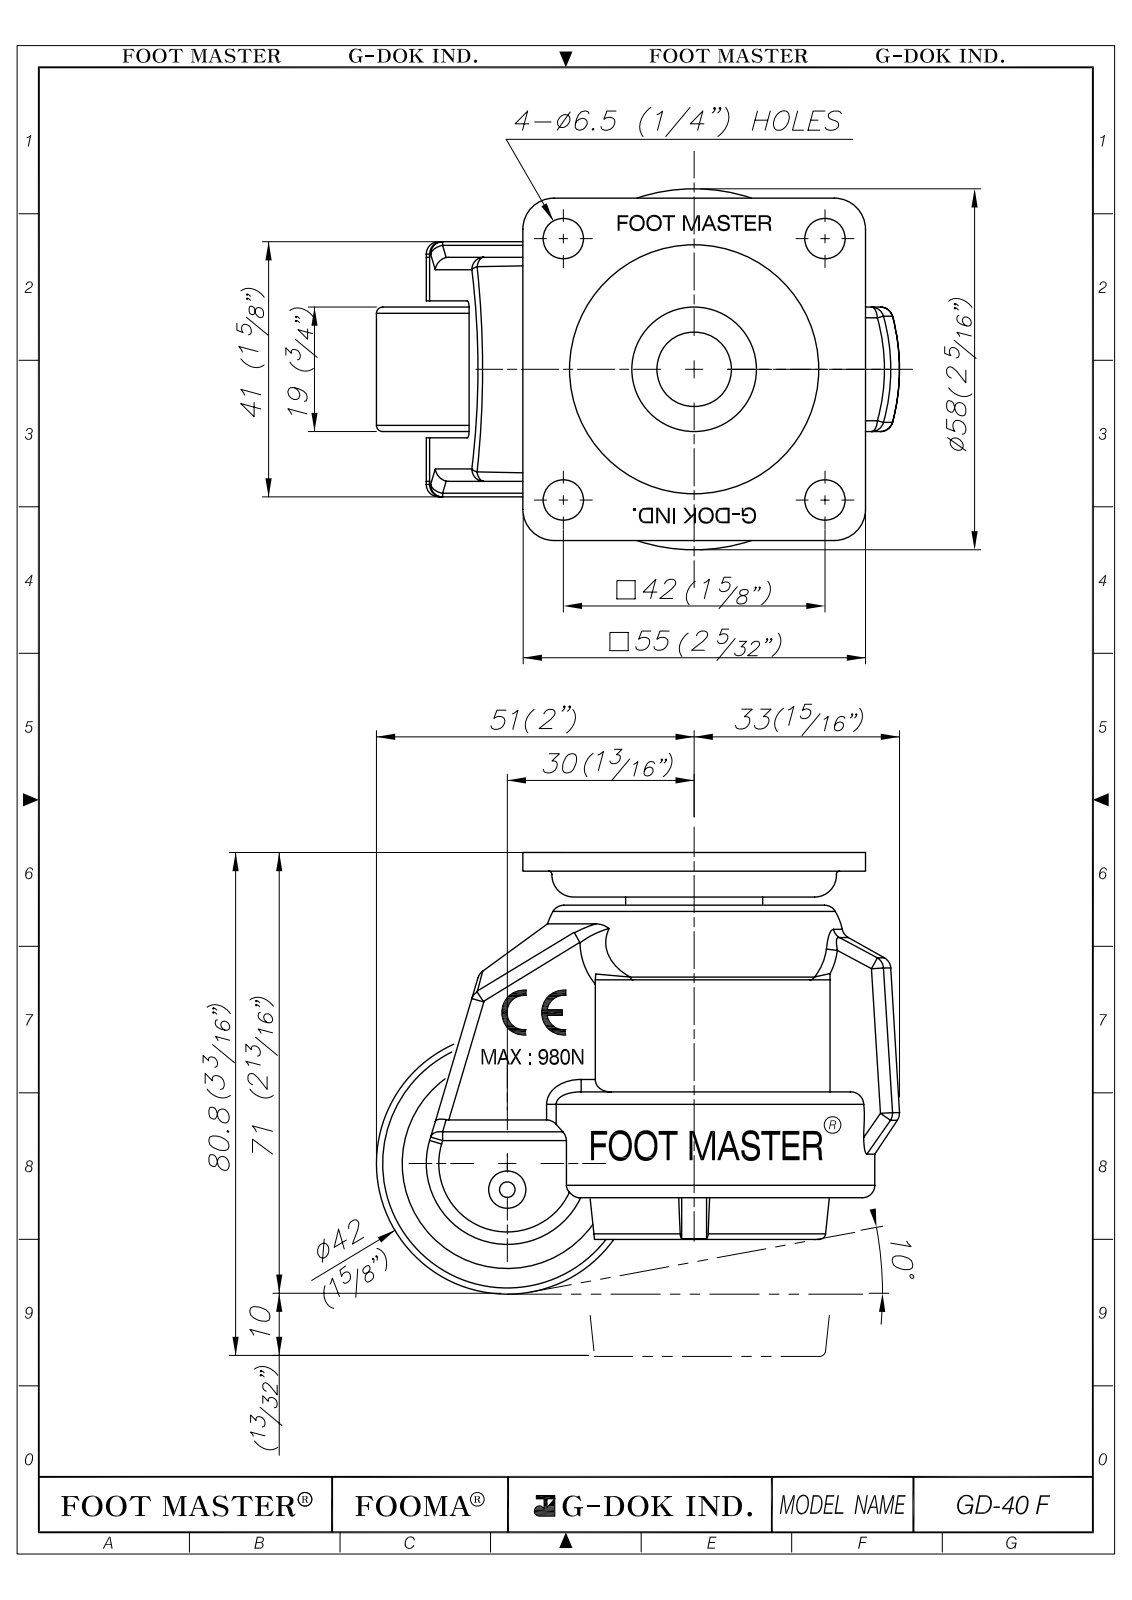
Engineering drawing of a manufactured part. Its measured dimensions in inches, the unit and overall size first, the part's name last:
Units: inches
Overall size (bounding box): 3.306 × 2.795 × 2.283
Round holes (diameter × count): ⌀0.256 ×4, ⌀0.236 ×2, ⌀0.252 ×1, ⌀0.276 ×1, ⌀0.28 ×1, ⌀0.433 ×1, ⌀0.709 ×1, ⌀0.866 ×1, ⌀1.26 ×1, ⌀1.89 ×1
Round bosses / shafts (diameter × count): ⌀0.102 ×3, ⌀1.654 ×1, ⌀1.181 ×1, ⌀0.925 ×1, ⌀0.787 ×1, ⌀0.591 ×1, ⌀0.315 ×1, ⌀0.276 ×1
Partial cylindrical surfaces — rounded edges, fillets, slot ends (radius × count): R0.02 ×85, R0.039 ×58, R0.197 ×5, R0.079 ×4, R0.049 ×1, R0.103 ×1, R0.142 ×1, R0.512 ×1
Main face-to-face distances: 0.276, 0.039, 0.315, 0.118, 0.827, 1.142, 1.102, 0.866, 0.374, 0.236
Hole centre spacings: 1.169, 1.654, 2.339, 0.043, 0.176, 0.219
Volume: 7.404 in³ · Surface area: 79.86 in²
Bodies: 4 solids, 1265 faces (368 planar, 288 cylindrical, 609 other)
Part name (STEP PRODUCT): GD-40F
STEP written by: Autodesk Inventor 2009 (AUTOMOTIVE_DESIGN)
